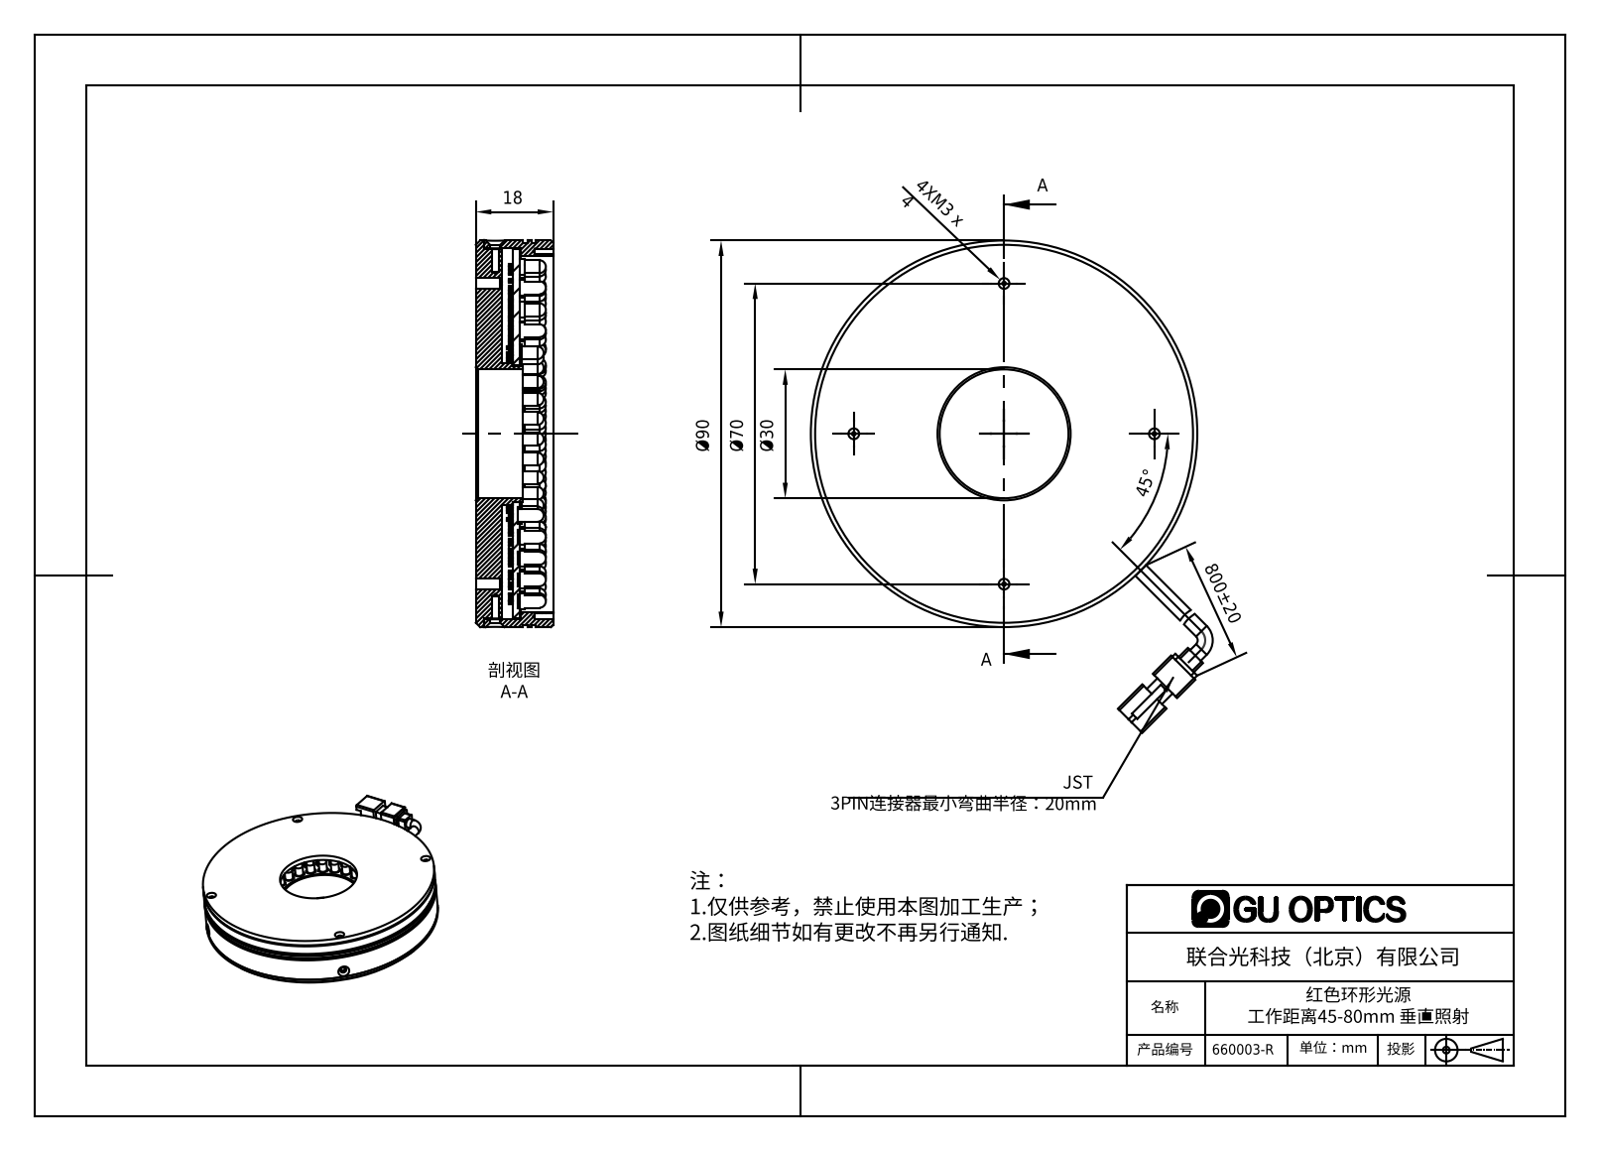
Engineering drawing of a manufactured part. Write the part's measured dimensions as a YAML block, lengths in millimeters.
part_name: "660003-R"
step_written_by: "SolidWorks 2016 (AUTOMOTIVE_DESIGN)"
units: millimeters
bodies: {solids: 181, faces: 3232, planar: 2184, cylindrical: 822, other: 226}
overall_size: [114.65, 93.59, 22.45]
volume: 70927
surface_area: 64656
round_holes:
  - {diameter: 3.1, count: 5}
  - {diameter: 1.25, count: 4}
  - {diameter: 1.7, count: 4}
  - {diameter: 2.5, count: 4}
  - {diameter: 1.6, count: 2}
  - {diameter: 2.4, count: 2}
  - {diameter: 30, count: 1}
  - {diameter: 32, count: 1}
  - {diameter: 83, count: 1}
  - {diameter: 86.4, count: 1}
round_bosses_or_shafts:
  - {diameter: 3.8, count: 175}
  - {diameter: 3, count: 175}
  - {diameter: 3.5, count: 2}
  - {diameter: 90, count: 1}
  - {diameter: 89, count: 1}
  - {diameter: 86, count: 1}
  - {diameter: 33, count: 1}
  - {diameter: 31.6, count: 1}
partial_cylinders:
  - {radius: 0.5, count: 12}
  - {radius: 1, count: 4}
  - {radius: 1.65, count: 1}
  - {radius: 6, count: 1}
face_to_face_distances: [2, 7.7, 18, 8.7, 11.3, 9.3, 9.7, 6, 10.3, 20]
hole_center_spacings: [55.06, 5, 7.5, 35, 42.5, 49.5, 60.1, 77.5]
